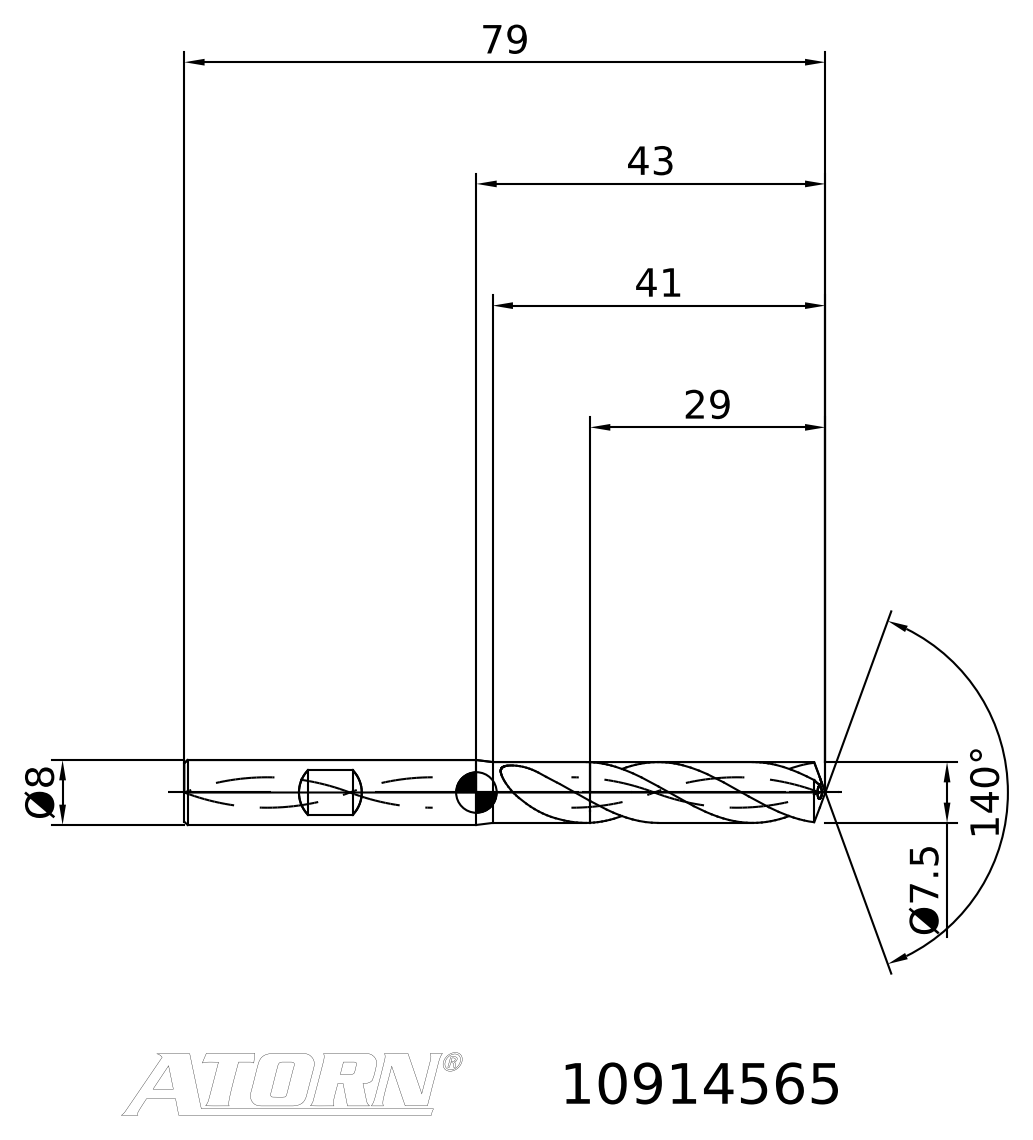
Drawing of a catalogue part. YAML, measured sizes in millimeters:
step_written_by: "TDM (AUTOMOTIVE_DESIGN)"
units: millimeters
bodies: {solids: 2, faces: 32, planar: 8, cylindrical: 0, other: 24}
overall_size: [79, 19.56, 11.66]
volume: 3089
surface_area: 2111
face_to_face_distances: [50, 27.98, 77.98]
